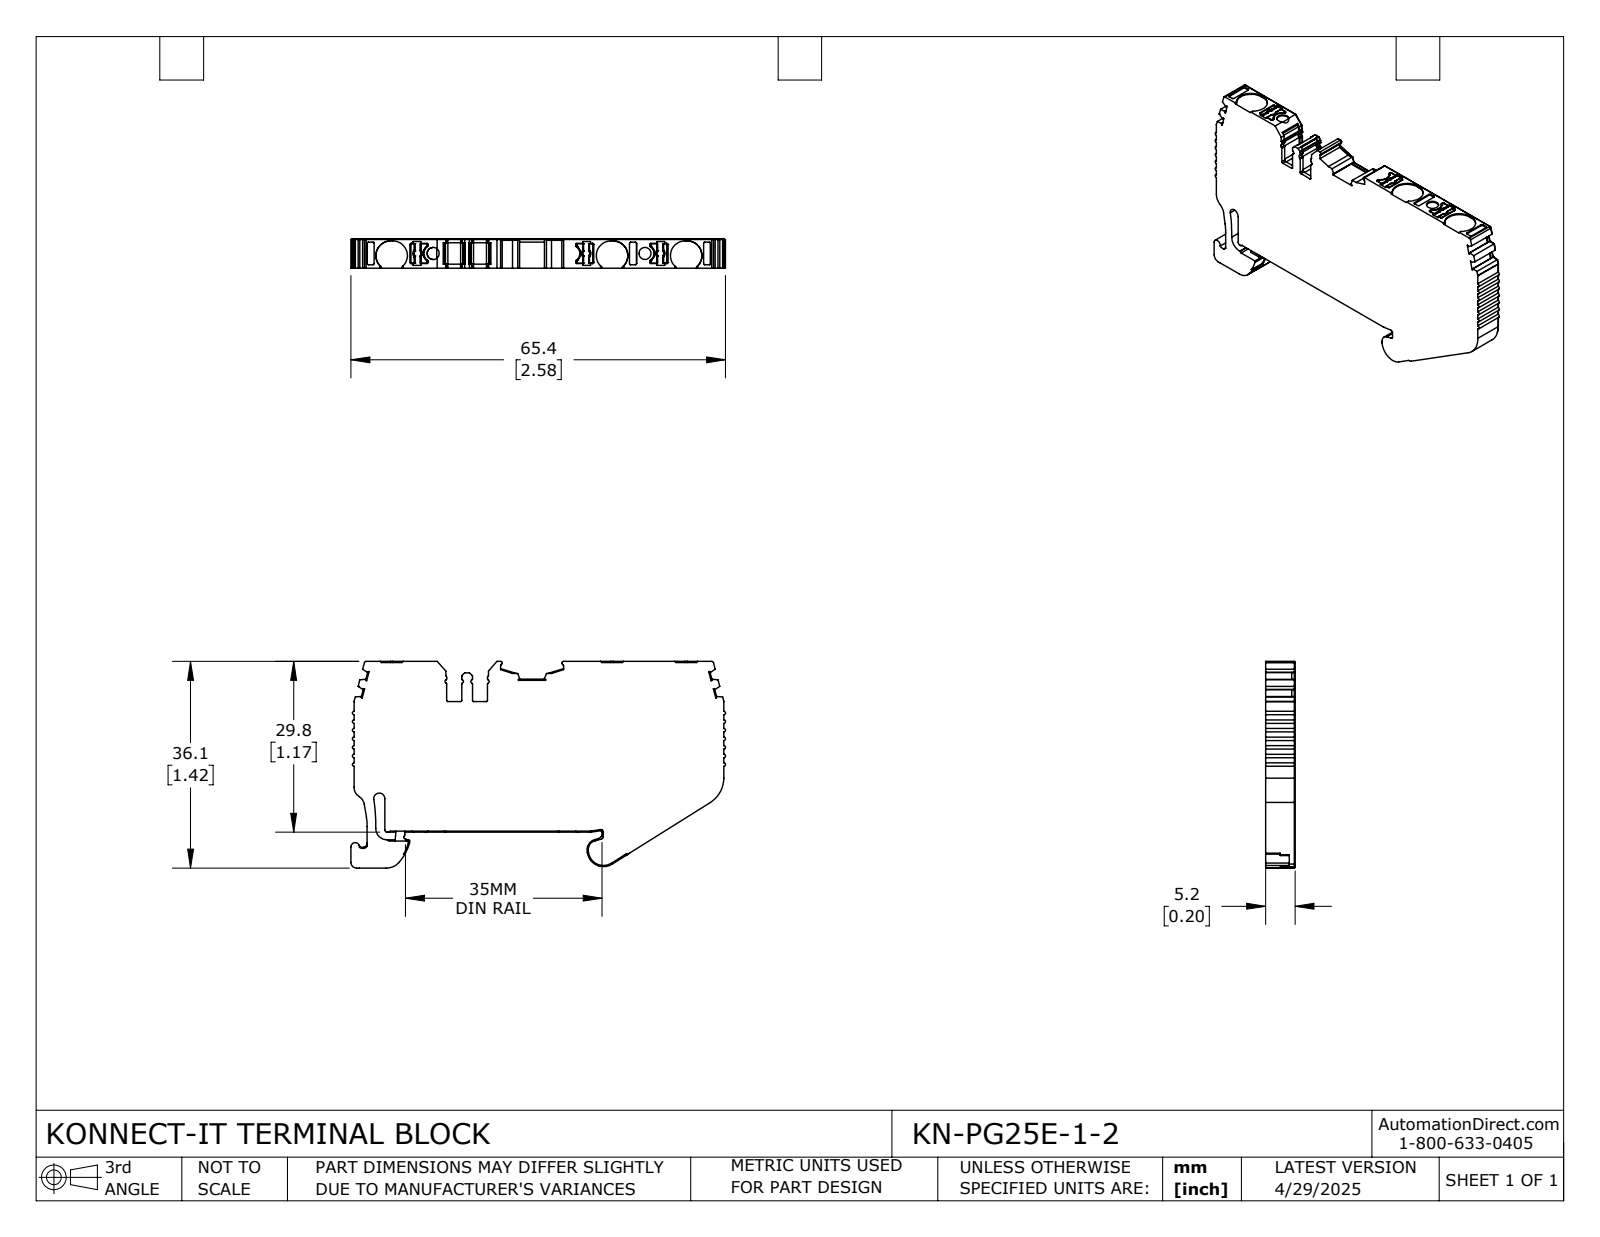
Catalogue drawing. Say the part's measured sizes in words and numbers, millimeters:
The part is named "KN-PG25E-1-2". Its 3-D file was written by "SolidWorks 2024 (CONFIG_CONTROL_DESIGN)". It is 1 solid with 708 faces: 373 planar, 282 cylindrical and 53 other. Overall it measures 65.42 by 36.07 by 5.15 millimeters. Its volume is 9 532 cubic millimeters and its surface area 5 187 square millimeters. Round holes: 2 of diameter 2.1. Partial cylindrical surfaces (rounded edges, fillets, slot ends): 65 of radius 0.2, 42 of radius 0.3, 19 of radius 0.1, 17 of radius 0.4, 16 of radius 0.5, 12 of radius 0.15, 8 of radius 1, 6 of radius 2.55. The main face-to-face distances are 5.15, 29.61, 29.81, 29.41, 64.58, 4.5, 5, 1.2, 5.37, 59.21. The hole center spacings are 36.98.
